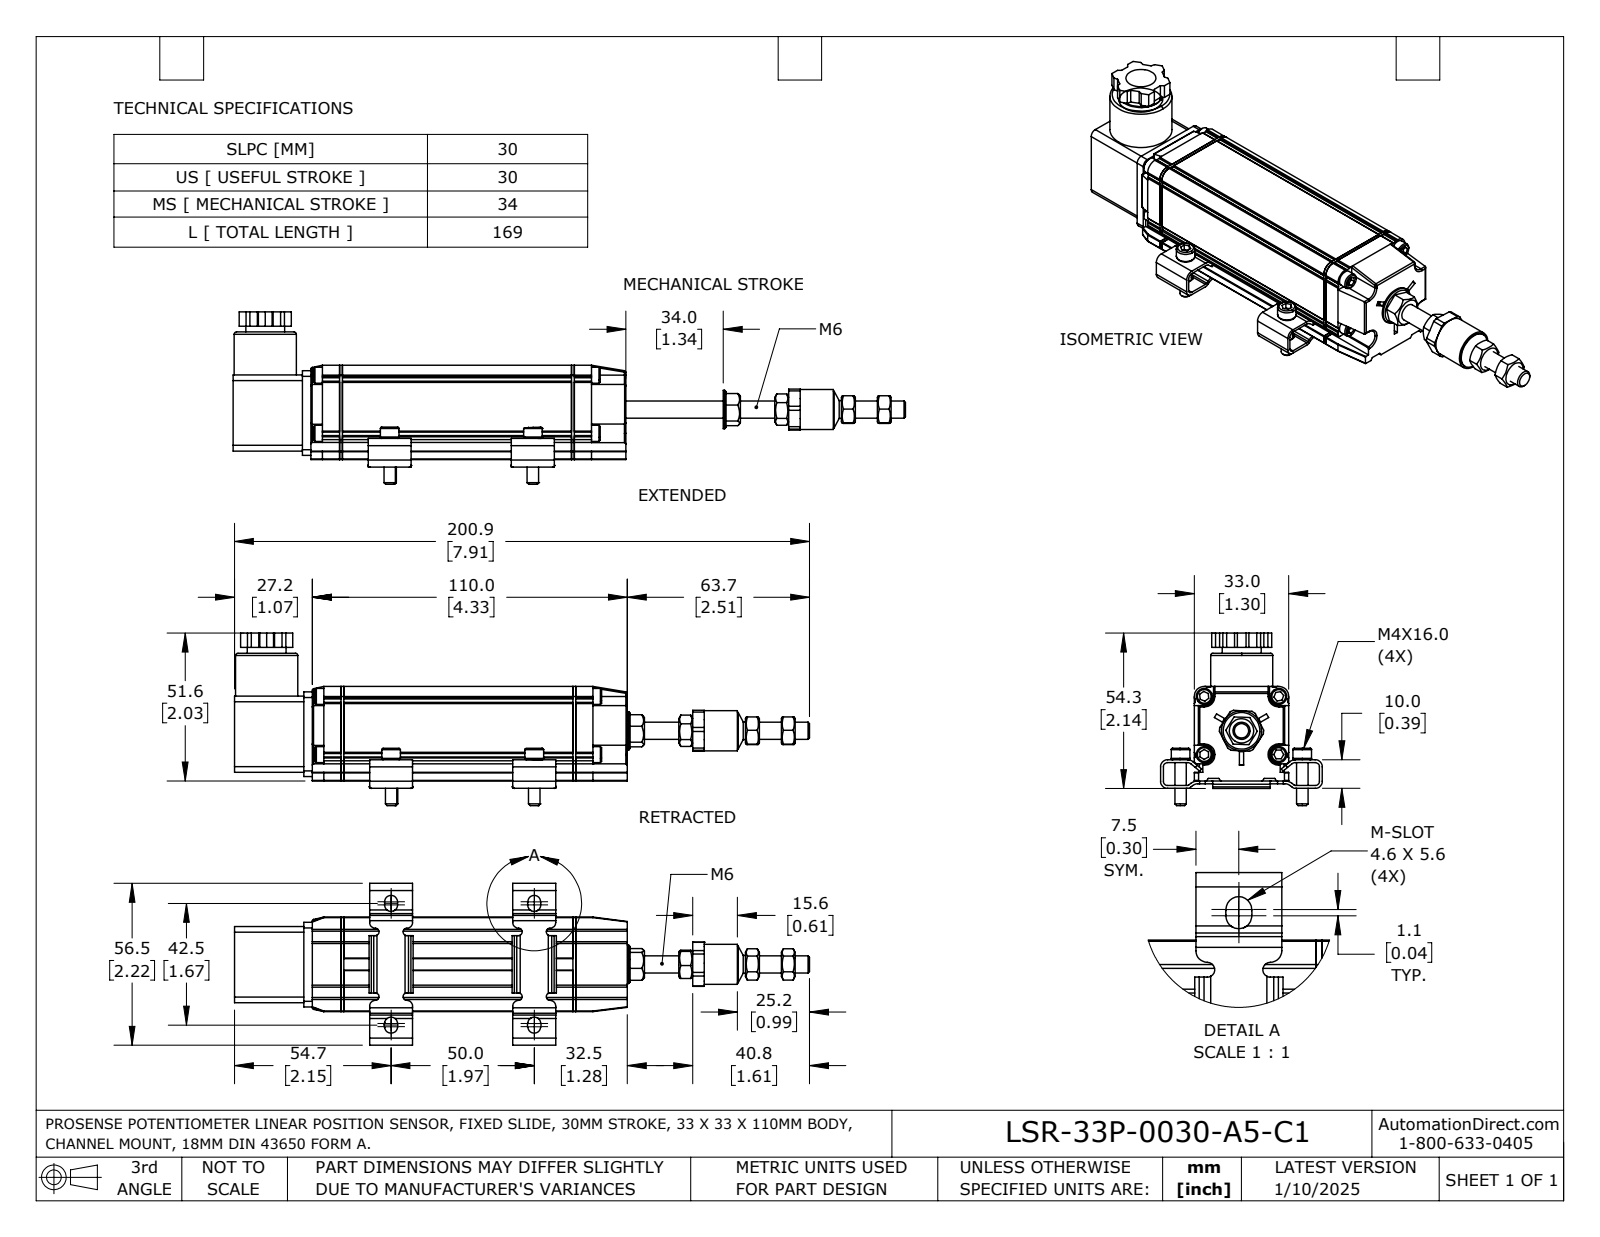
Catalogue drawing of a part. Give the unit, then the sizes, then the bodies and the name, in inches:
Units: inches
Overall size (bounding box): 7.907 × 2.37 × 2.224
Round holes (diameter × count): ⌀0.118 ×4, ⌀0.169 ×1, ⌀0.205 ×1, ⌀0.209 ×1, ⌀0.232 ×1, ⌀0.276 ×1, ⌀0.285 ×1, ⌀0.394 ×1, ⌀0.413 ×1, ⌀0.573 ×1, ⌀0.602 ×1, ⌀0.866 ×1
Round bosses / shafts (diameter × count): ⌀0.157 ×5, ⌀0.256 ×4, ⌀0.22 ×4, ⌀0.13 ×4, ⌀0.106 ×4, ⌀0.854 ×1, ⌀0.551 ×1, ⌀0.535 ×1
Partial cylindrical surfaces — rounded edges, fillets, slot ends (radius × count): R0.079 ×28, R0.02 ×23, R0.008 ×16, R0.051 ×8, R0.059 ×8, R0.089 ×8, R0.118 ×8, R0.039 ×4
Main face-to-face distances: 1.299, 0.039, 0.118, 0.063, 0.22, 0.102, 0.984, 1.181, 0.079, 0.394
Hole centre spacings: 0.047, 0.583, 0.607, 0.696, 0.73, 0.799, 1.024, 1.299
Bodies: 0 solids, 888 faces (568 planar, 252 cylindrical, 68 other)
Part name (STEP PRODUCT): LSR-33P-0030-A5-C1
STEP written by: SolidWorks 2023 (AUTOMOTIVE_DESIGN)
